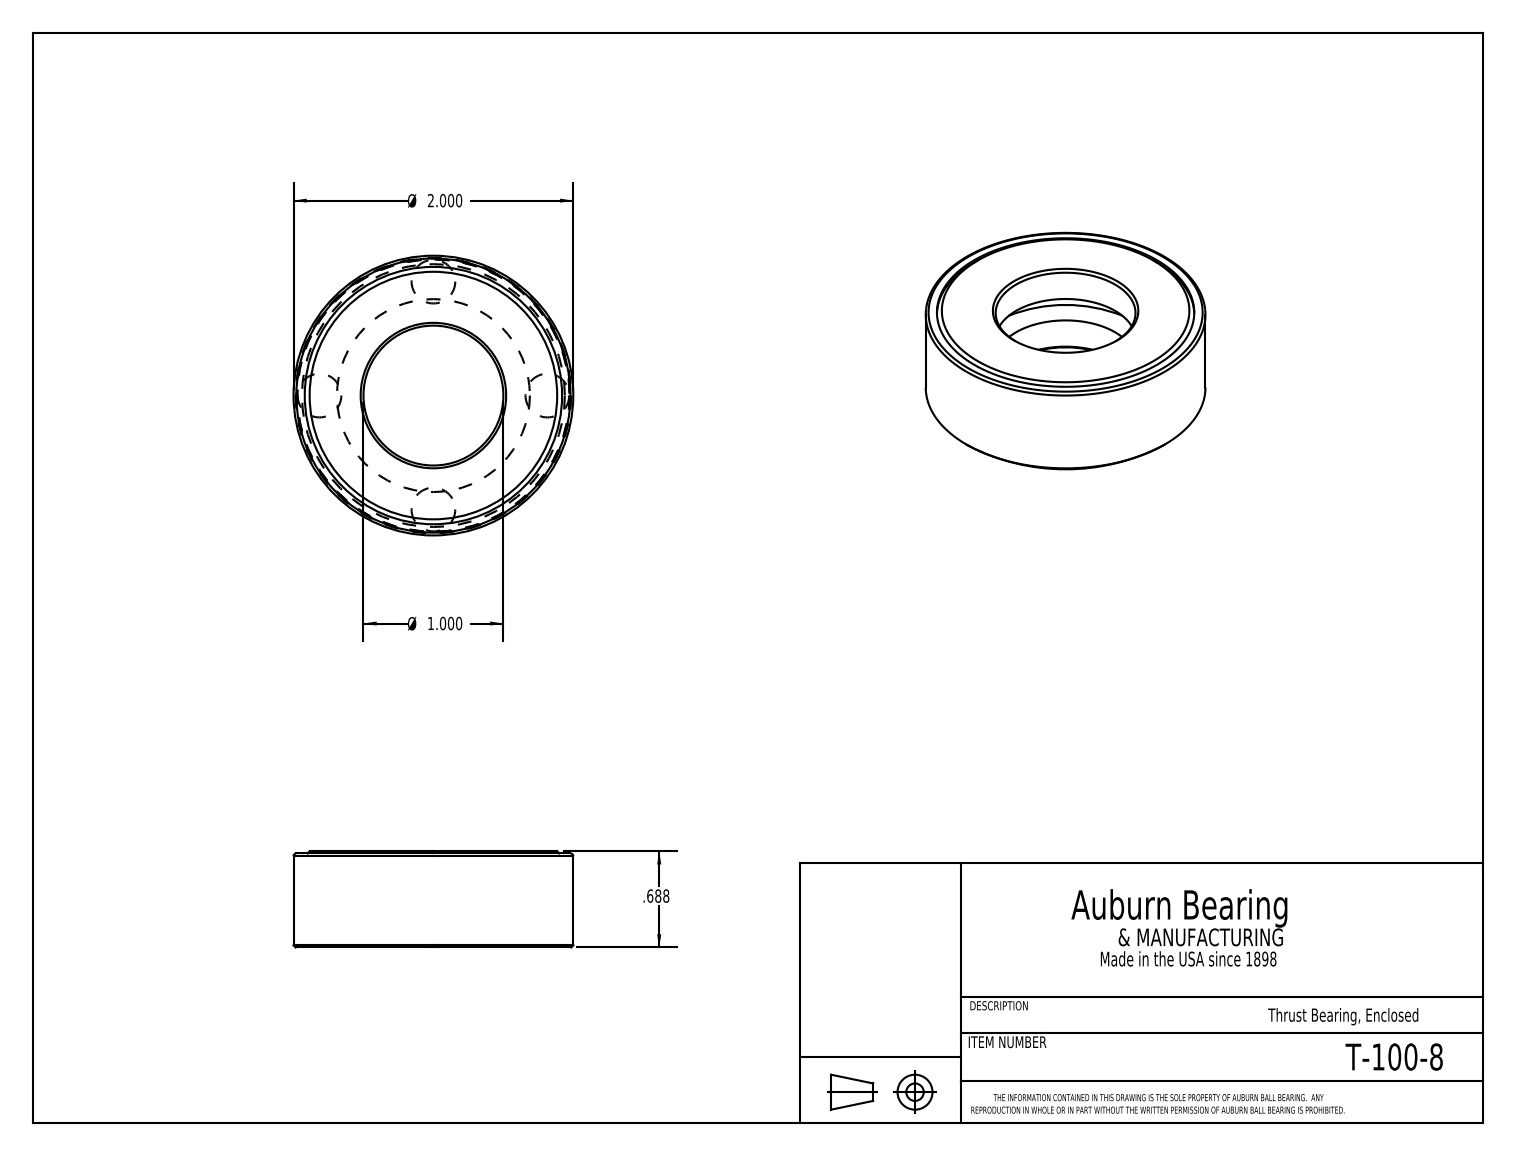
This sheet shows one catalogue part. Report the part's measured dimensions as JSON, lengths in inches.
{"part_name": "T-100-8", "step_written_by": "SolidWorks 2016 (CONFIG_CONTROL_DESIGN)", "units": "inches", "bodies": {"solids": 6, "faces": 28, "planar": 9, "cylindrical": 7, "other": 12}, "overall_size": [2, 2, 0.688], "volume_in3": 1.123, "surface_area_in2": 20.9, "round_holes": [[1, 1], [1.84, 1], [1.96, 1]], "round_bosses_or_shafts": [[2, 1], [1.946, 1]], "face_to_face_distances": [0.25, 0.437, 0.687, 0.187, 0.652, 0.402, 0.215, 0.035, 0.672, 0.422]}
